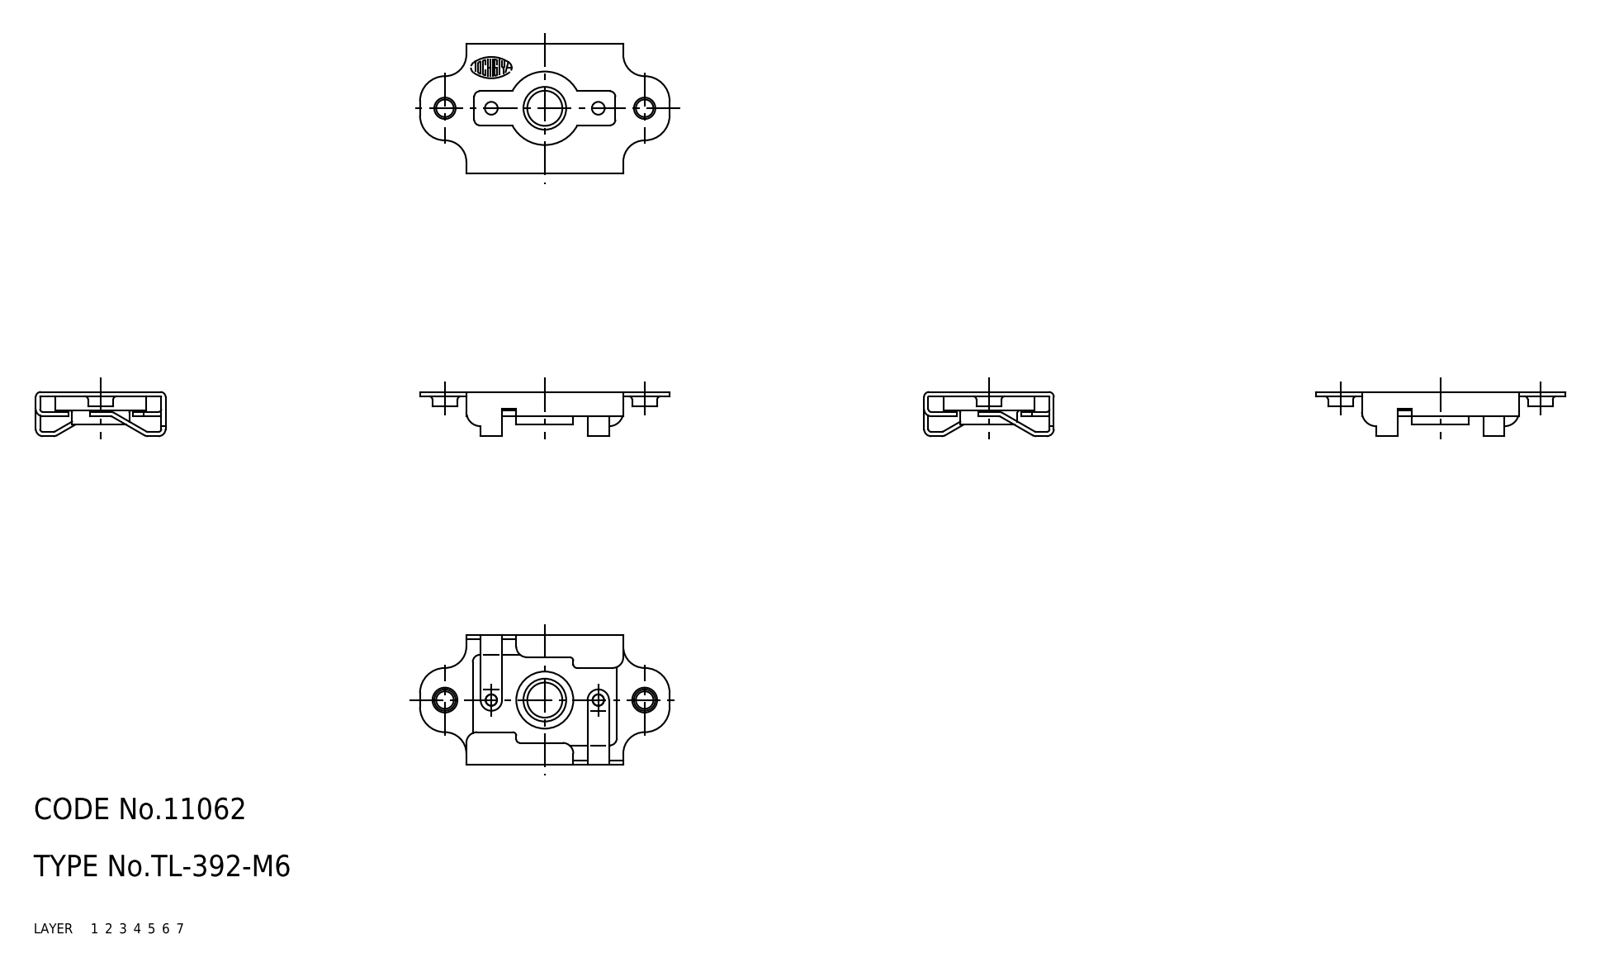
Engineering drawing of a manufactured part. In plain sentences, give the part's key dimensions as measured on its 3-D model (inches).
The part is named "67116017". Its 3-D file was written by "CADfix (AUTOMOTIVE_DESIGN)". It is 1 solid with 137 faces: 0 planar, 0 cylindrical and 137 other. Overall it measures 1.378 by 0.717 by 0.244 inches. Its volume is 0.055 cubic inches and its surface area 3.019 square inches.
